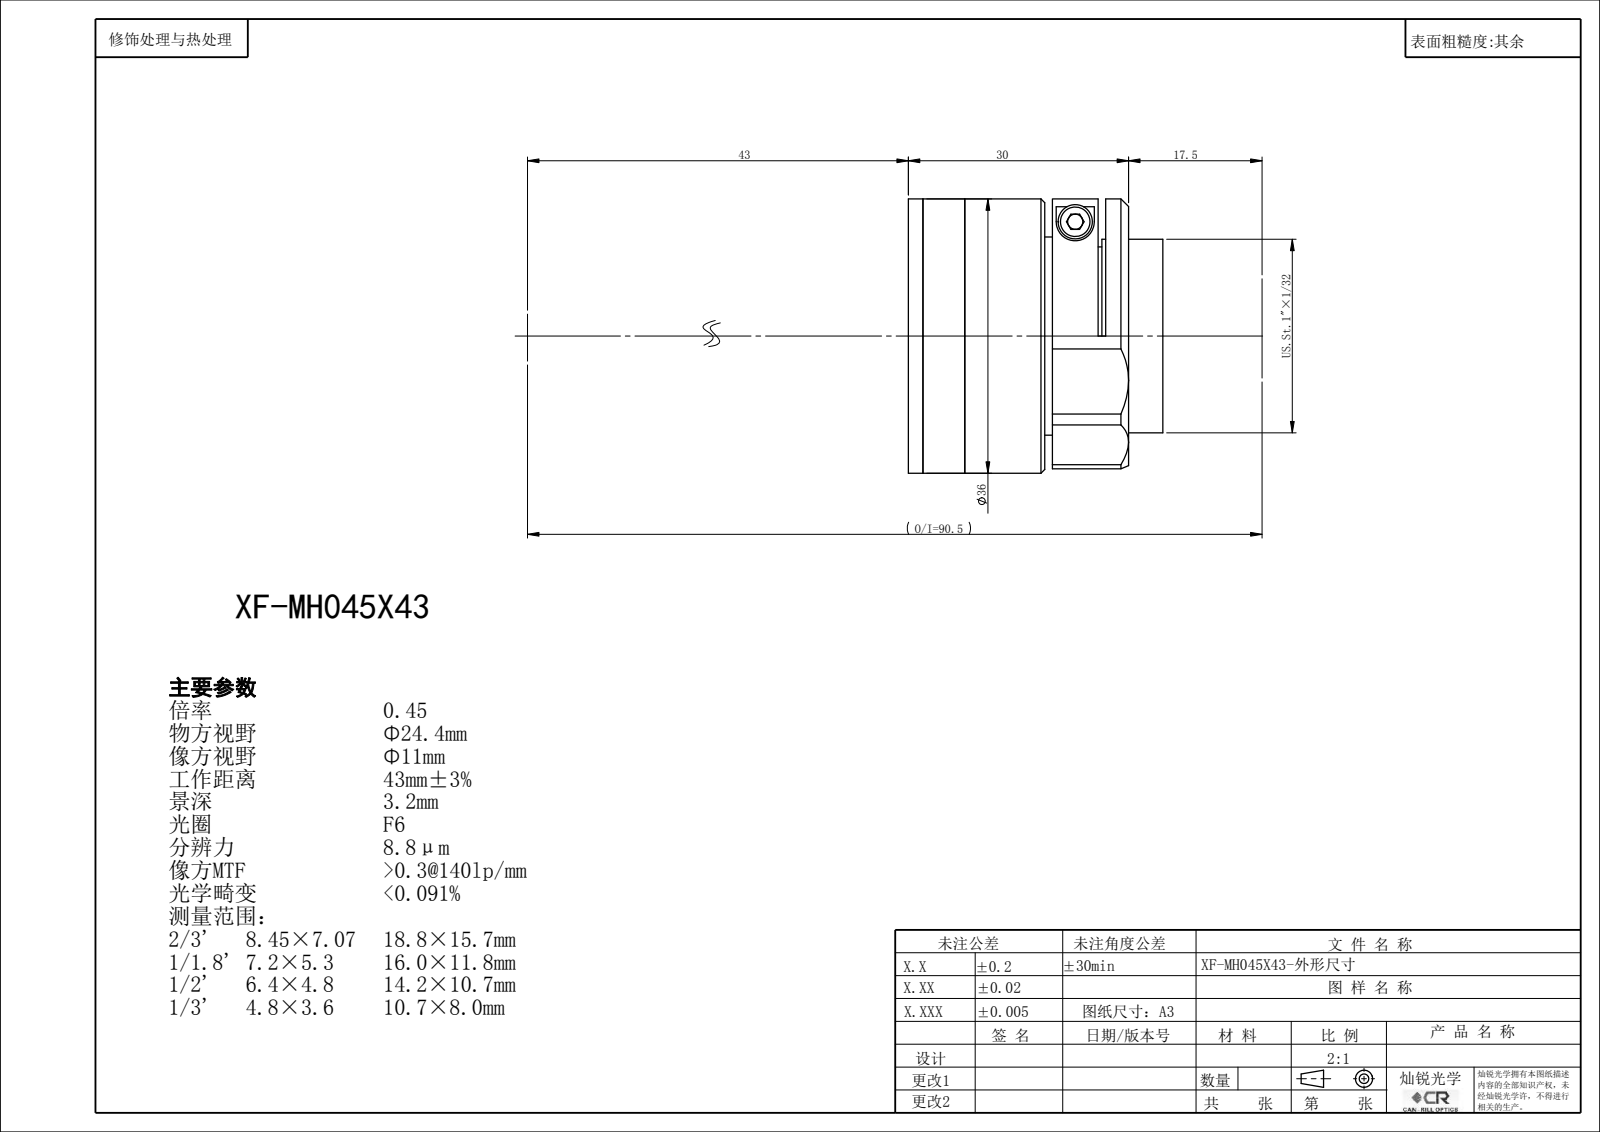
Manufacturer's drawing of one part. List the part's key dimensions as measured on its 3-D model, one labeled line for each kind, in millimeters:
Part name (STEP PRODUCT): XF-MH045X43
STEP written by: SolidWorks 2022 (CONFIG_CONTROL_DESIGN)
Units: millimetres
Bodies: 14 solids, 240 faces (92 planar, 102 cylindrical, 46 other)
Overall size (bounding box): 36 × 36 × 33.98
Volume: 20 455 mm³ · Surface area: 17 445 mm²
Round holes (diameter × count): ⌀2.5 ×3, ⌀3.22 ×1, ⌀6 ×1, ⌀7 ×1, ⌀7.4 ×1, ⌀8.4 ×1, ⌀10 ×1, ⌀12 ×1, ⌀14 ×1, ⌀16 ×1, ⌀18 ×1, ⌀20 ×1
Round bosses / shafts (diameter × count): ⌀3 ×3, ⌀36 ×1, ⌀34 ×1, ⌀28 ×1, ⌀27 ×1, ⌀25.4 ×1, ⌀9 ×1, ⌀8 ×1
Main face-to-face distances: 5.5, 8, 28.07, 22.57, 1.91, 7.41, 29.98, 2.5, 26.57, 1.5
